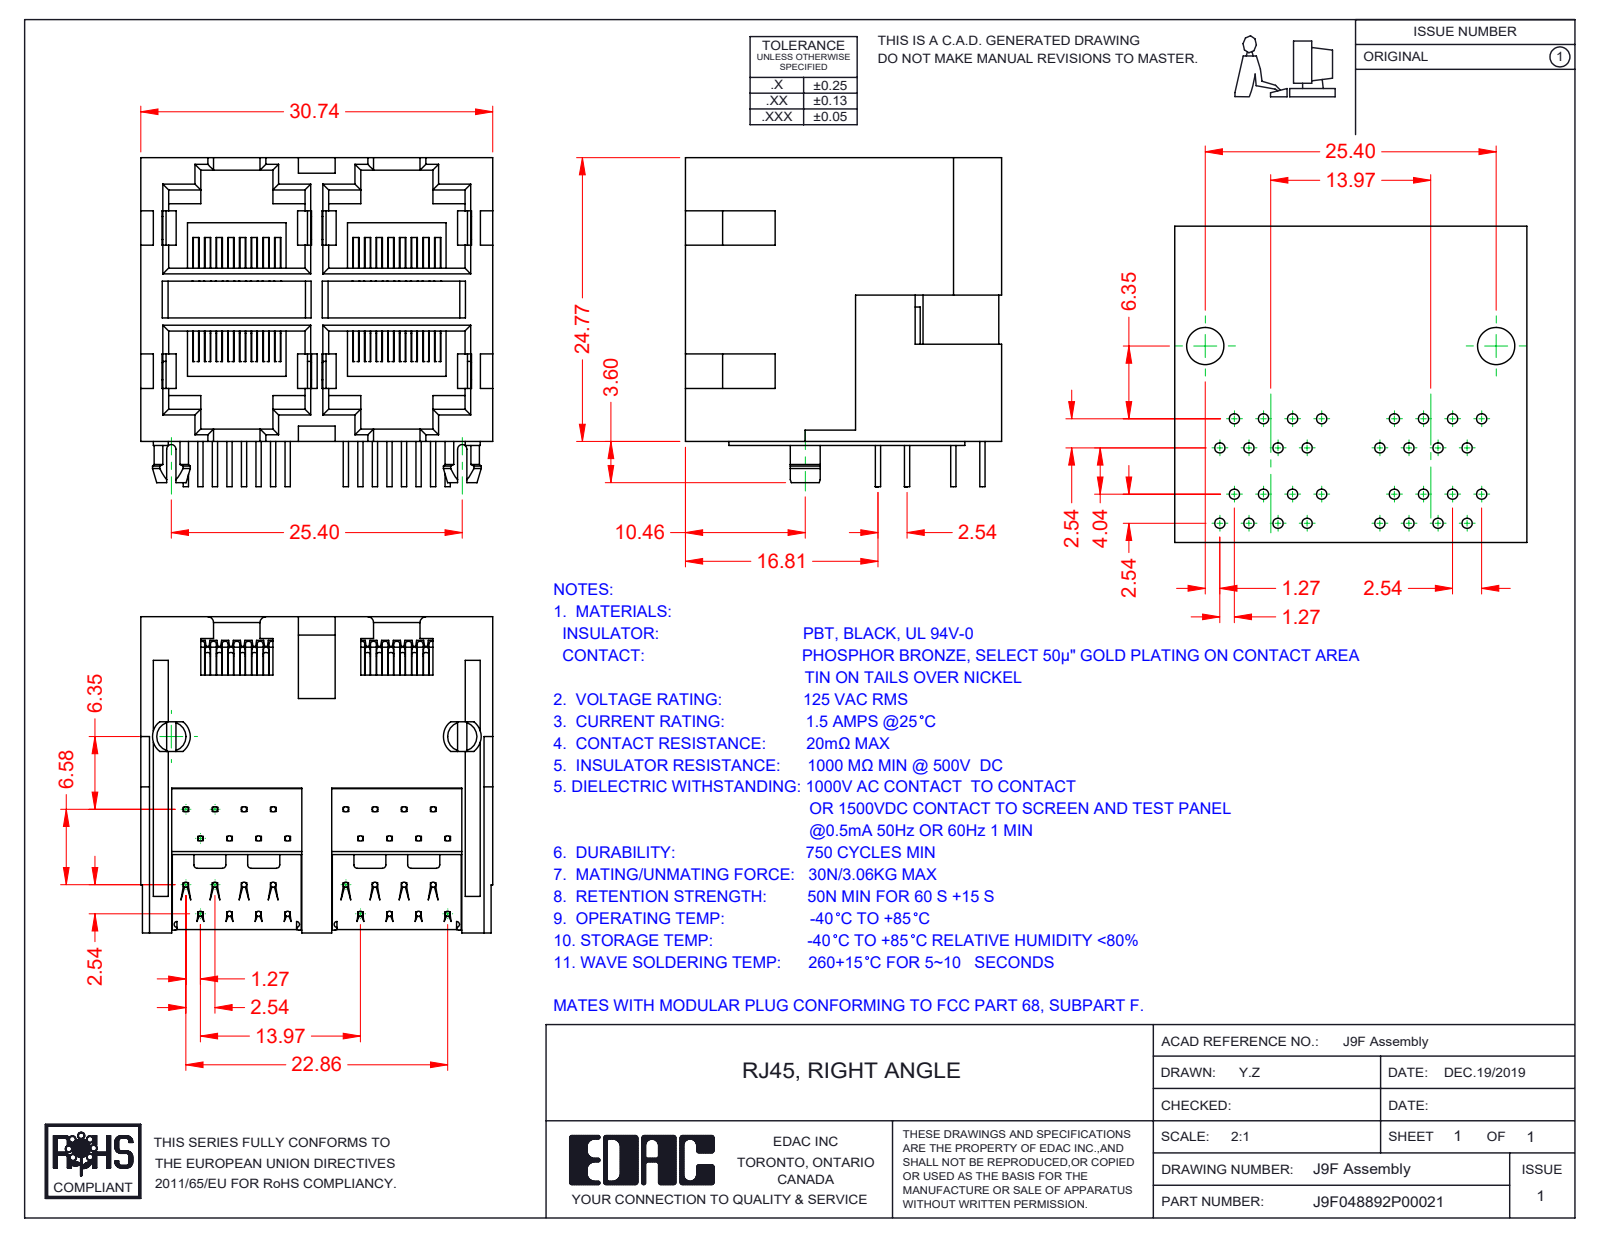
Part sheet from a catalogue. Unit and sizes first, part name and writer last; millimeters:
Units: millimetres
Overall size (bounding box): 30.74 × 28.71 × 27.6
Round bosses / shafts (diameter × count): ⌀0.46 ×144
Partial cylindrical surfaces — rounded edges, fillets, slot ends (radius × count): R0.2 ×63, R0.5 ×25, R0.3 ×9, R0.25 ×4, R0.4 ×2, R0.45 ×2, R1.5 ×2, R1.65 ×2
Main face-to-face distances: 13.97, 1, 0.35, 12.7, 15, 13.05, 11.98, 1.05, 13.62, 5.5
Volume: 11 763 mm³ · Surface area: 19 774 mm²
Bodies: 37 solids, 2810 faces (1899 planar, 557 cylindrical, 354 other)
Part name (STEP PRODUCT): 9F Insulator; 9F Contacts Lower; 9F Contact Lock Upper; RJ9F048892P00021 (+2 more)
STEP written by: SolidWorks 2016 (CONFIG_CONTROL_DESIGN)
